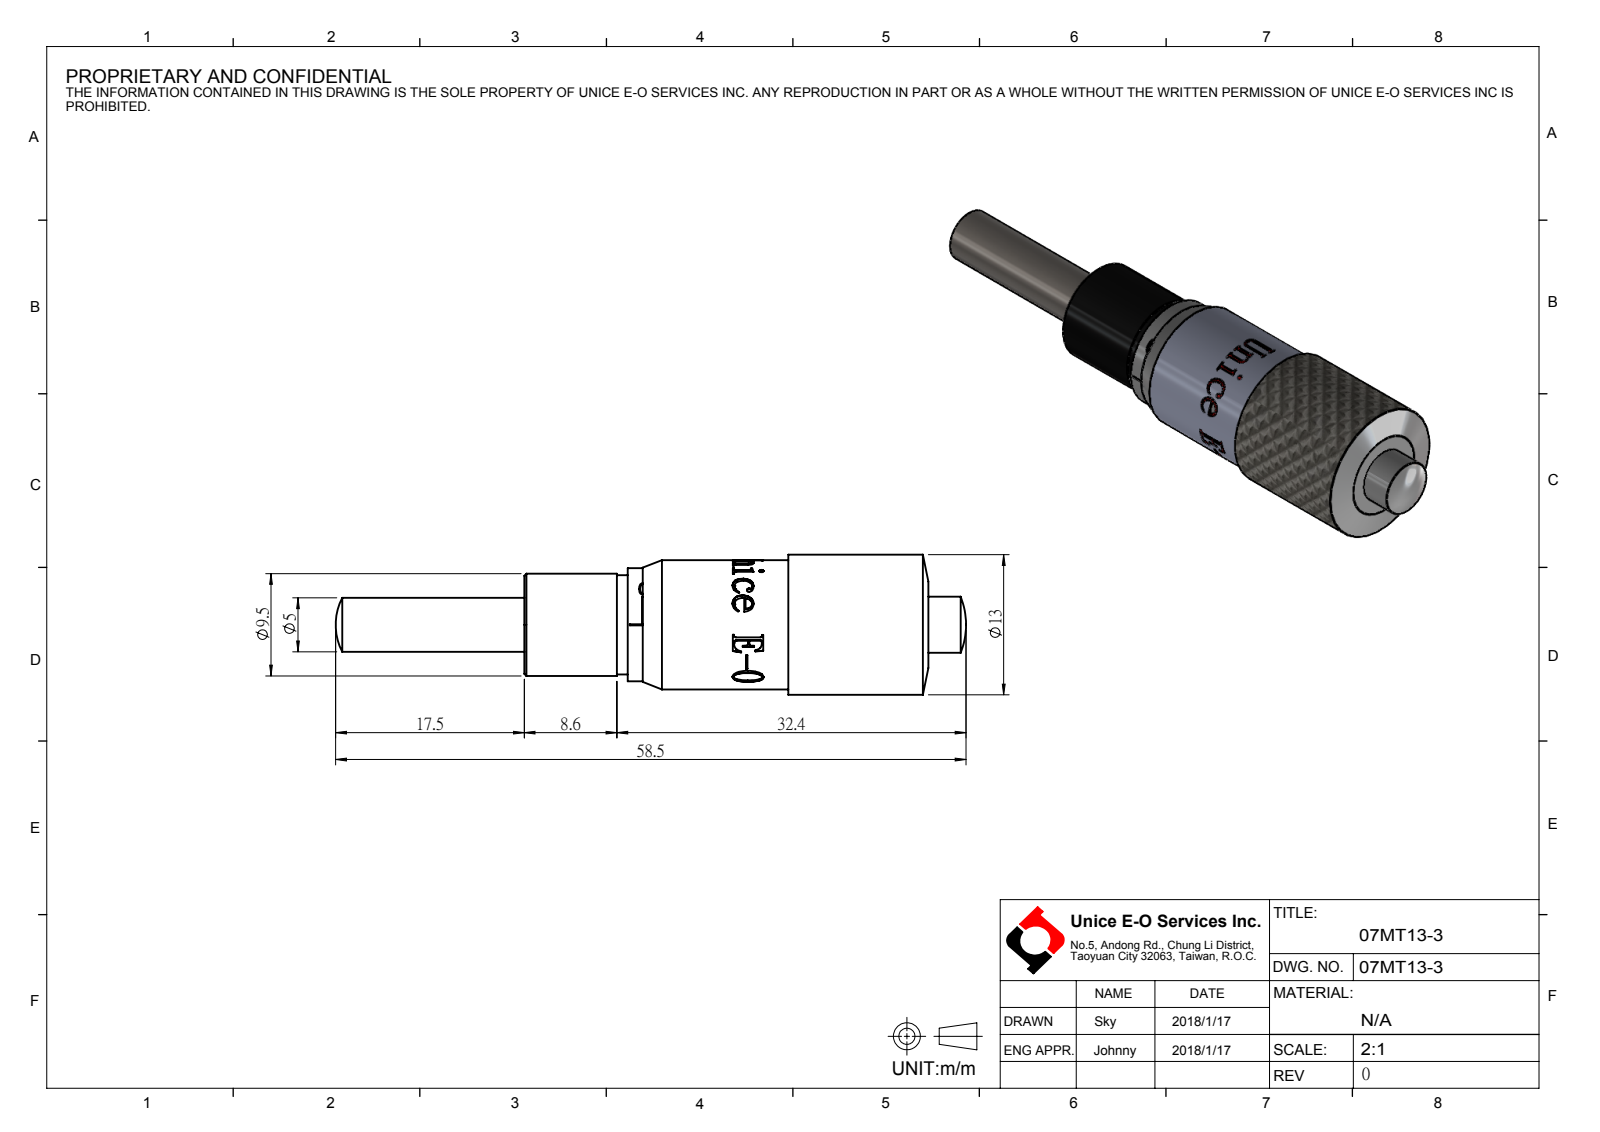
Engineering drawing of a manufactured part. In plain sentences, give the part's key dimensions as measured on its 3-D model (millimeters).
The part is named "07MT13-3". Its 3-D file was written by "SolidWorks 2016 (AUTOMOTIVE_DESIGN)". It is 0 solids with 93 faces: 23 planar, 26 cylindrical and 44 other. Overall it measures 58.5 by 13 by 13 millimeters. Round bosses or shafts: 1 of diameter 13, 1 of diameter 12, 1 of diameter 10.5, 1 of diameter 9.5, 1 of diameter 9.2, 1 of diameter 5.2, 1 of diameter 5. Partial cylindrical surfaces (rounded edges, fillets, slot ends): 1 of radius 5.98. The main face-to-face distances are 37.5, 9.6, 27.9, 24.5, 14.9, 13, 8.6, 1, 15.9, 28.9.
